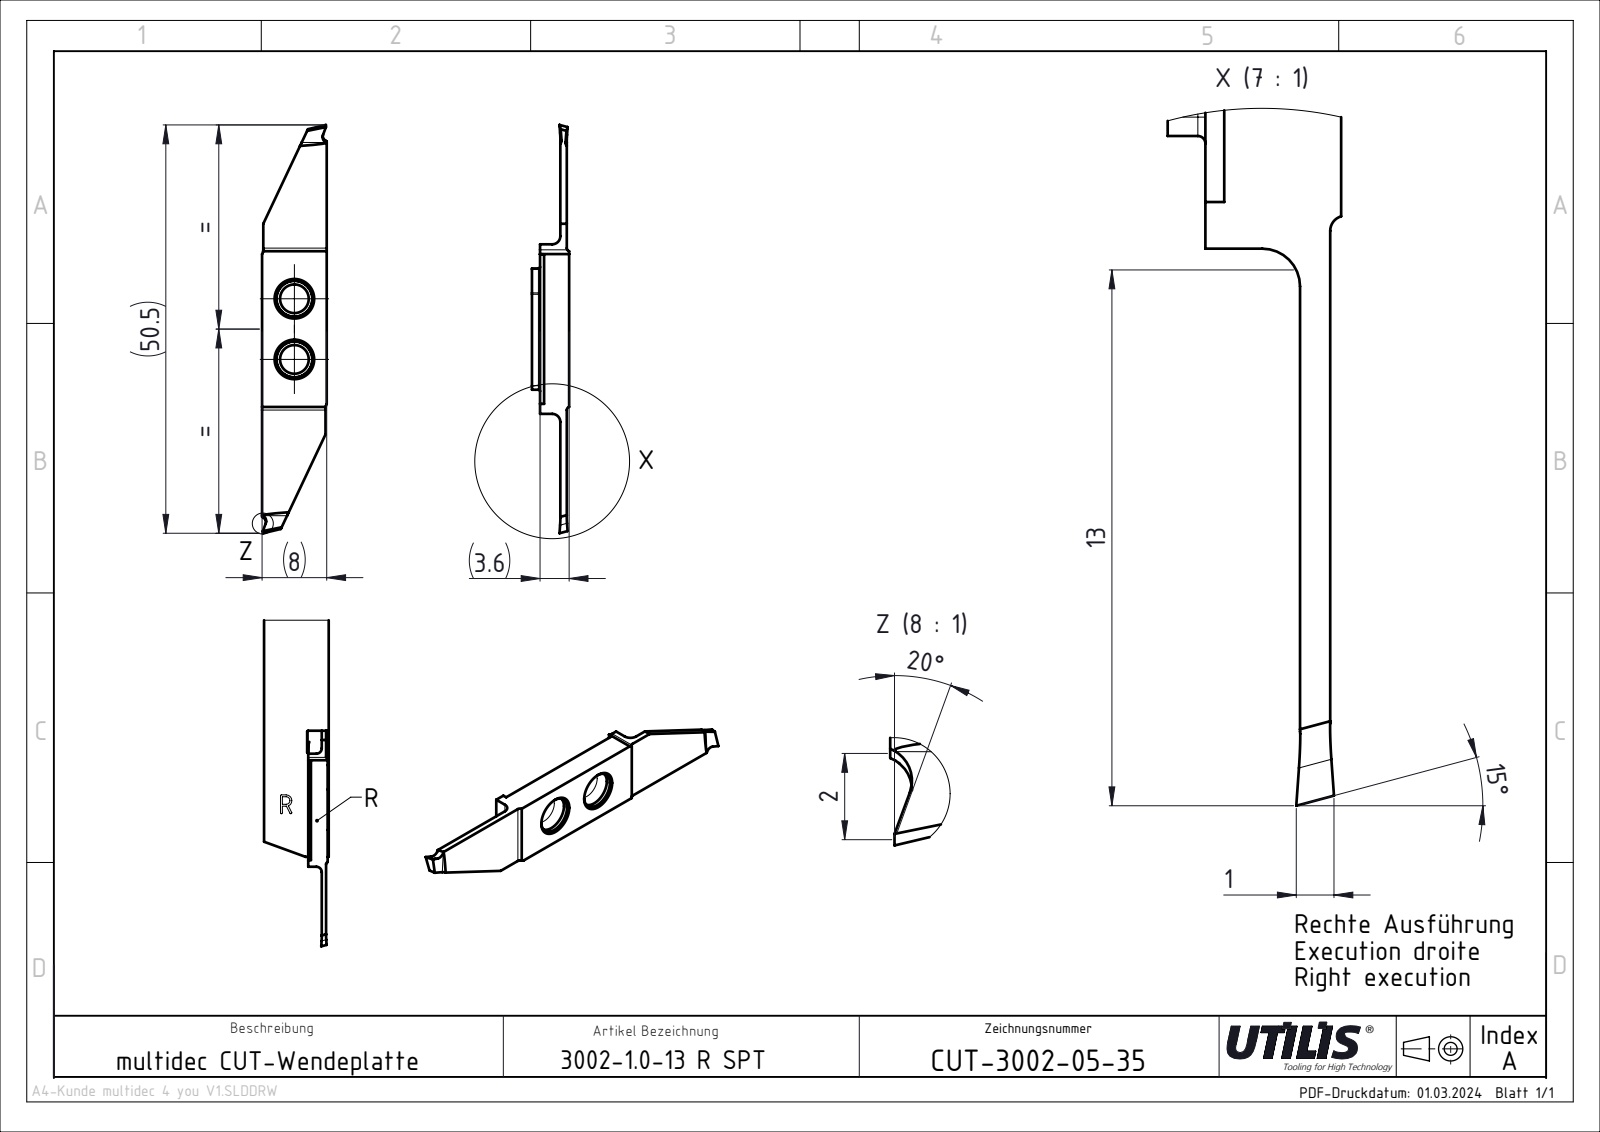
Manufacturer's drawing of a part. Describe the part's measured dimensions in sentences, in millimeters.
The part is named "CUT-3002 SPT Slim_and_Deep; ASME Y14.5". Its 3-D file was written by "SolidWorks 2023 SP4 || FormatWorks Professional (AP242_MANAGED_MODEL_BASED_3D_ENGINEERING_MIM_LF)". It is 1 solid with 36 faces: 26 planar, 10 cylindrical and 0 other. Overall it measures 50.5 by 8 by 3.6 millimeters. Its volume is 656 cubic millimeters and its surface area 926 square millimeters. Round holes: 2 of diameter 3.55. Partial cylindrical surfaces (rounded edges, fillets, slot ends): 4 of radius 1, 2 of radius 0.4. The main face-to-face distances are 0.8, 1.09, 2.51, 3.31, 3.6, 8, 20.98, 18.09, 7.85, 1.61. The hole center spacings are 7.5.
